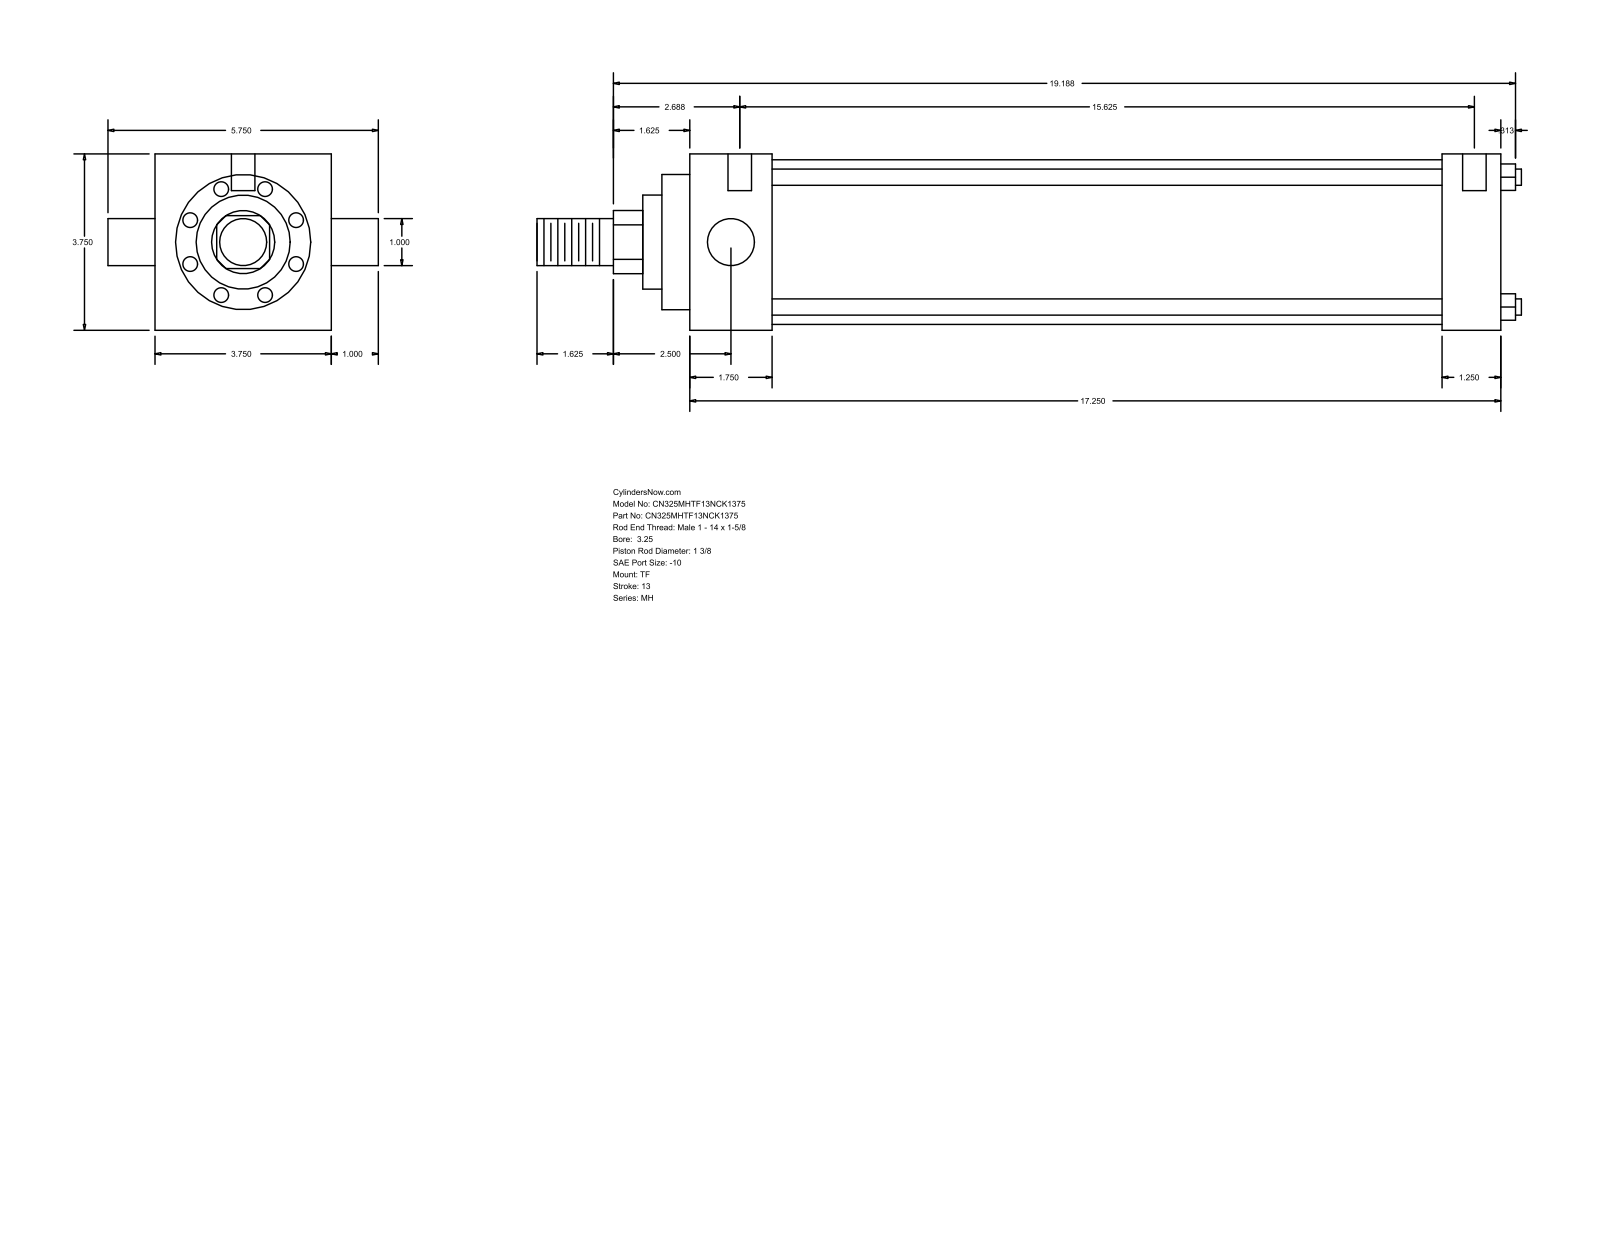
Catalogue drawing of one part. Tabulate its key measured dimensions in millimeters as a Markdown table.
| quantity | value |
| --- | --- |
| part name | MH_TF__0325_1.375 |
| STEP written by | GSSL Pune (CONFIG_CONTROL_DESIGN) |
| units | millimeters |
| bodies | 0 solids, 86 faces (61 planar, 25 cylindrical, 0 other) |
| overall size | 531.81 × 146.05 × 95.25 |
| round holes (diameter × count) | 5.56 × 3, 12.7 × 2 |
| round bosses / shafts (diameter × count) | 8.76 × 4, 25.4 × 2, 88.9 × 1, 73.03 × 1, 50.8 × 1, 34.92 × 1 |
| partial cylindrical surfaces (radius × count) | 17.06 × 1 |
| main face-to-face distances | 95.24, 438.16, 44.45, 406.41, 361.96, 393.71, 31.75, 15.08, 59.53, 421.49 |
| hole center spacings | 1.59, 4.76, 396.88, 398.47, 401.64, 403.23 |
